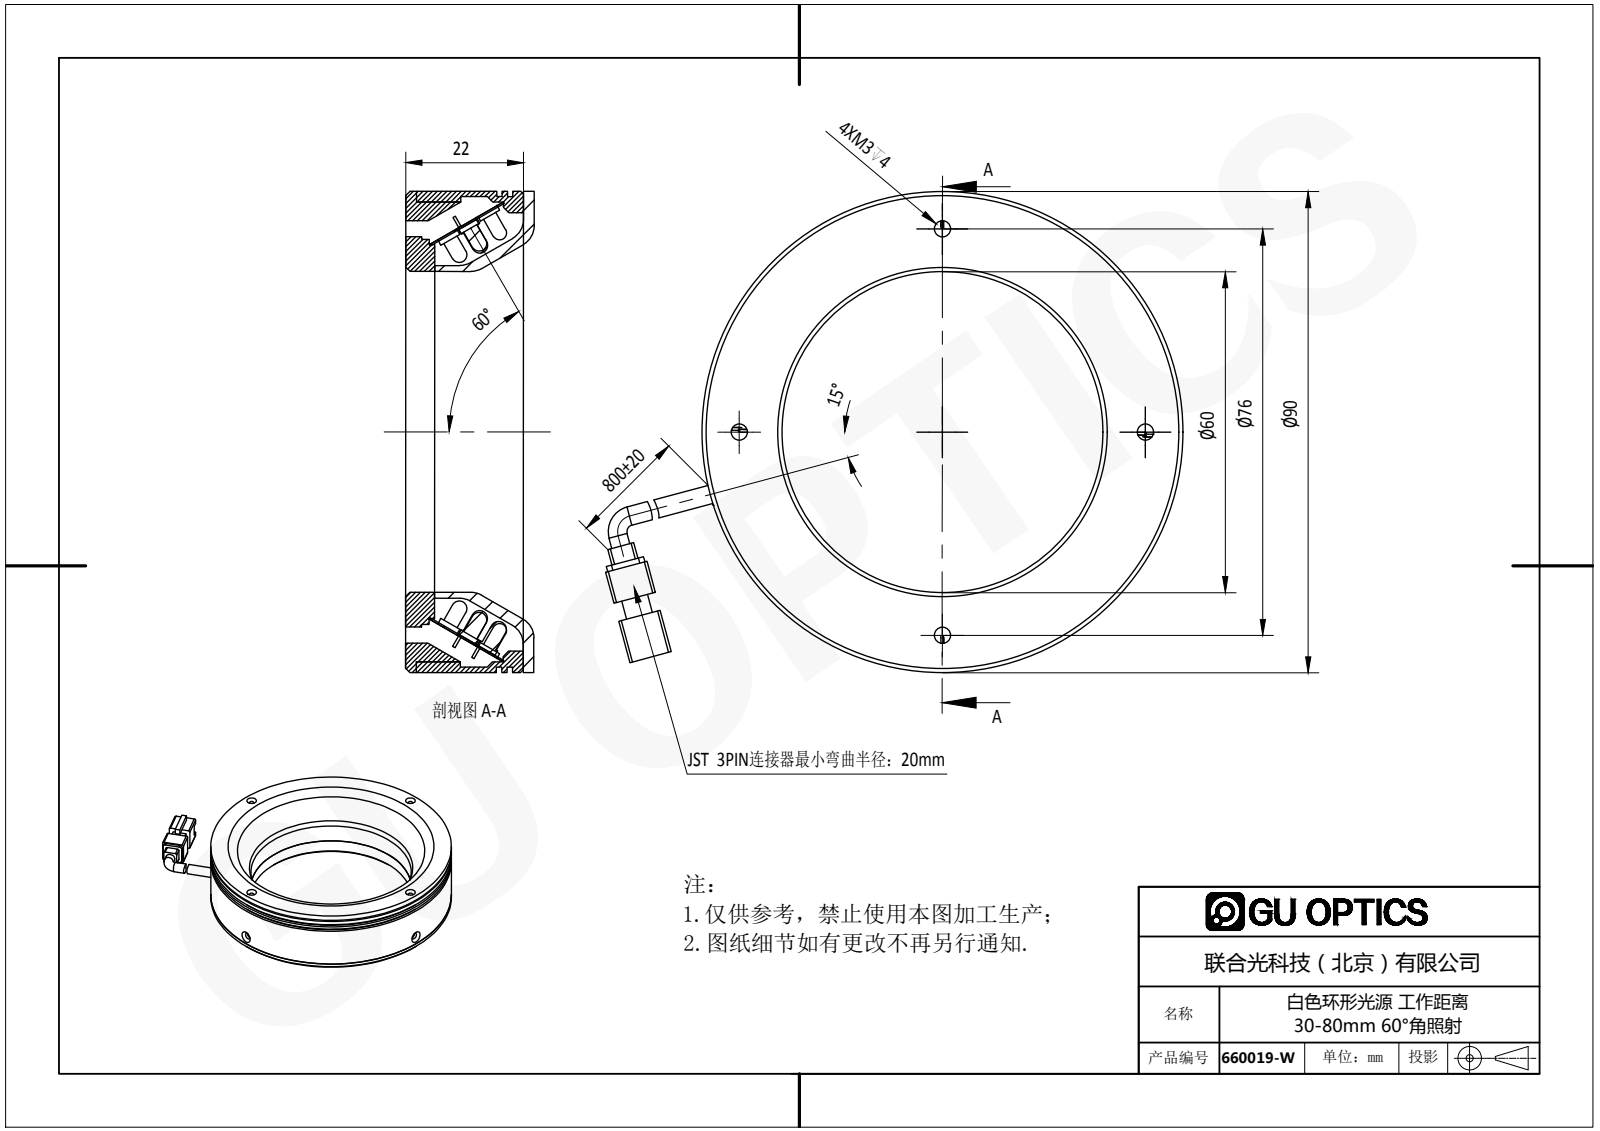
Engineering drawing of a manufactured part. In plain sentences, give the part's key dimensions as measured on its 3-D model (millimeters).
The part is named "660019-W". Its 3-D file was written by "SolidWorks 2016 (AUTOMOTIVE_DESIGN)". It is 153 solids with 2753 faces: 1844 planar, 708 cylindrical and 201 other. Overall it measures 116.8 by 90 by 24.45 millimeters. Its volume is 46 795 cubic millimeters and its surface area 61 171 square millimeters. Round holes: 4 of diameter 1.25, 4 of diameter 1.7, 4 of diameter 3, 3 of diameter 3.5, 2 of diameter 2, 2 of diameter 2.4, 1 of diameter 60, 1 of diameter 82, 1 of diameter 86. Round bosses or shafts: 147 of diameter 3.8, 147 of diameter 3, 2 of diameter 3.5, 1 of diameter 90, 1 of diameter 88, 1 of diameter 72, 1 of diameter 70, 1 of diameter 62.2. Partial cylindrical surfaces (rounded edges, fillets, slot ends): 8 of radius 0.5, 4 of radius 1, 1 of radius 1.65, 1 of radius 5. The main face-to-face distances are 2, 22, 1, 24, 3, 20, 5.4, 16.6, 18.6, 3.4. The hole center spacings are 30.84, 73.93, 38, 42, 53.74, 59.4, 76, 84.
